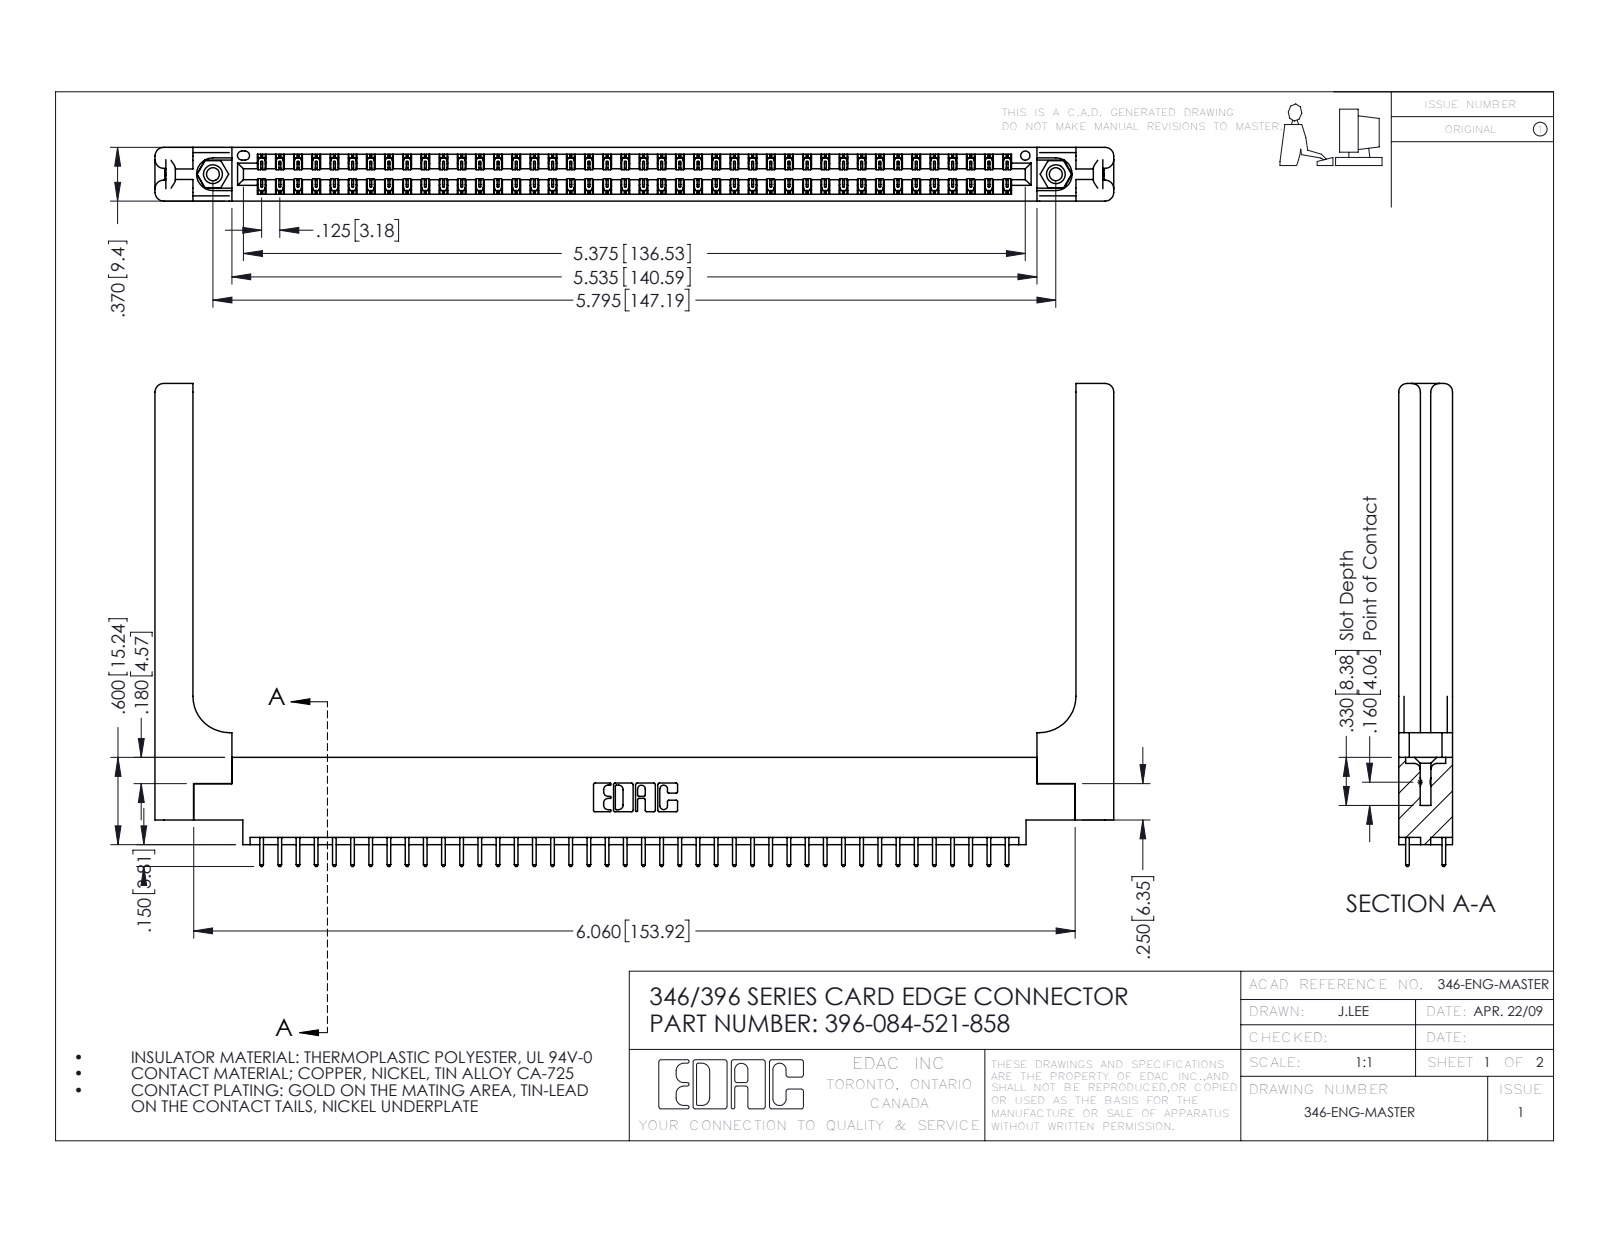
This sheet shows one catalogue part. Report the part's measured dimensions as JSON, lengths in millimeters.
{"part_name": "346-220-058_345-220-058; 345-250-001_345-250-001-102; 396-084-521-858; 346 Part_0.170 Offset - 0.156 Dia-TH (+1 more)", "step_written_by": "SolidWorks 2016 (CONFIG_CONTROL_DESIGN)", "units": "millimeters", "bodies": {"solids": 89, "faces": 4750, "planar": 3168, "cylindrical": 1522, "other": 60}, "overall_size": [167.4, 84.3, 9.4], "volume_mm3": 23630, "surface_area_mm2": 27100, "round_holes": [[2.3, 2], [3.2, 2], [4, 2], [1.6, 1]], "round_bosses_or_shafts": [[3.9, 2]], "partial_cylinders_radius": [[0.2, 126], [0.3, 84], [0.3, 22], [1.5, 16], [0.2, 6], [0.8, 6], [0.7, 3], [0.4, 2]], "face_to_face_distances": [9.4, 1.2, 8.2, 1.8, 3.8, 3.8, 6.4, 0.6, 7.6, 7], "hole_center_spacings": [6.2, 141.9, 147.2]}
